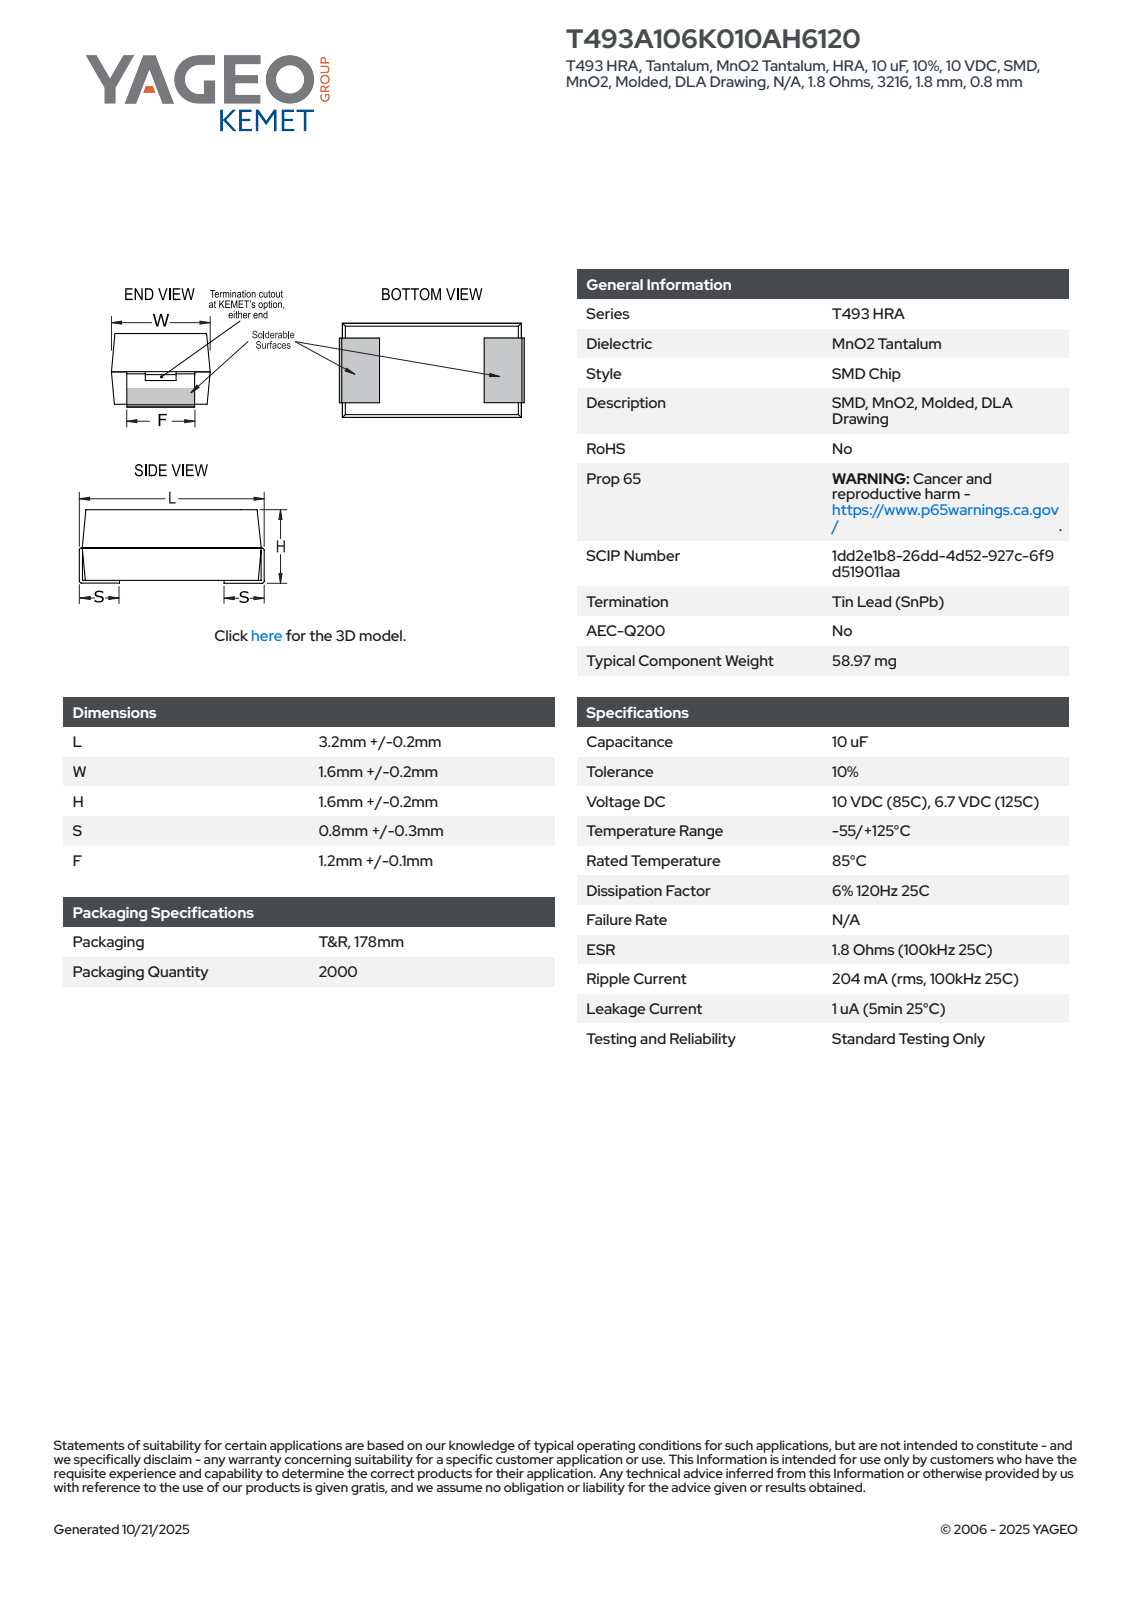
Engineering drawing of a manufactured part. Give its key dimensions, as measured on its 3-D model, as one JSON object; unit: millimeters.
{"part_name": "CTSM_Case_Top_21; CTSM_Case_Anode_21; CTSM_Case_Cathode_21; CTSM_Case_Bottom_21 (+1 more)", "step_written_by": "SolidWorks 2014 (AUTOMOTIVE_DESIGN)", "units": "millimeters", "bodies": {"solids": 7, "faces": 94, "planar": 90, "cylindrical": 4, "other": 0}, "overall_size": [3.4, 1.8, 1.8], "volume_mm3": 9, "surface_area_mm2": 47, "face_to_face_distances": [0.75, 1.67, 0.92, 1.8, 1.79, 3.27, 0.88, 3.13, 3.12, 0.85]}
